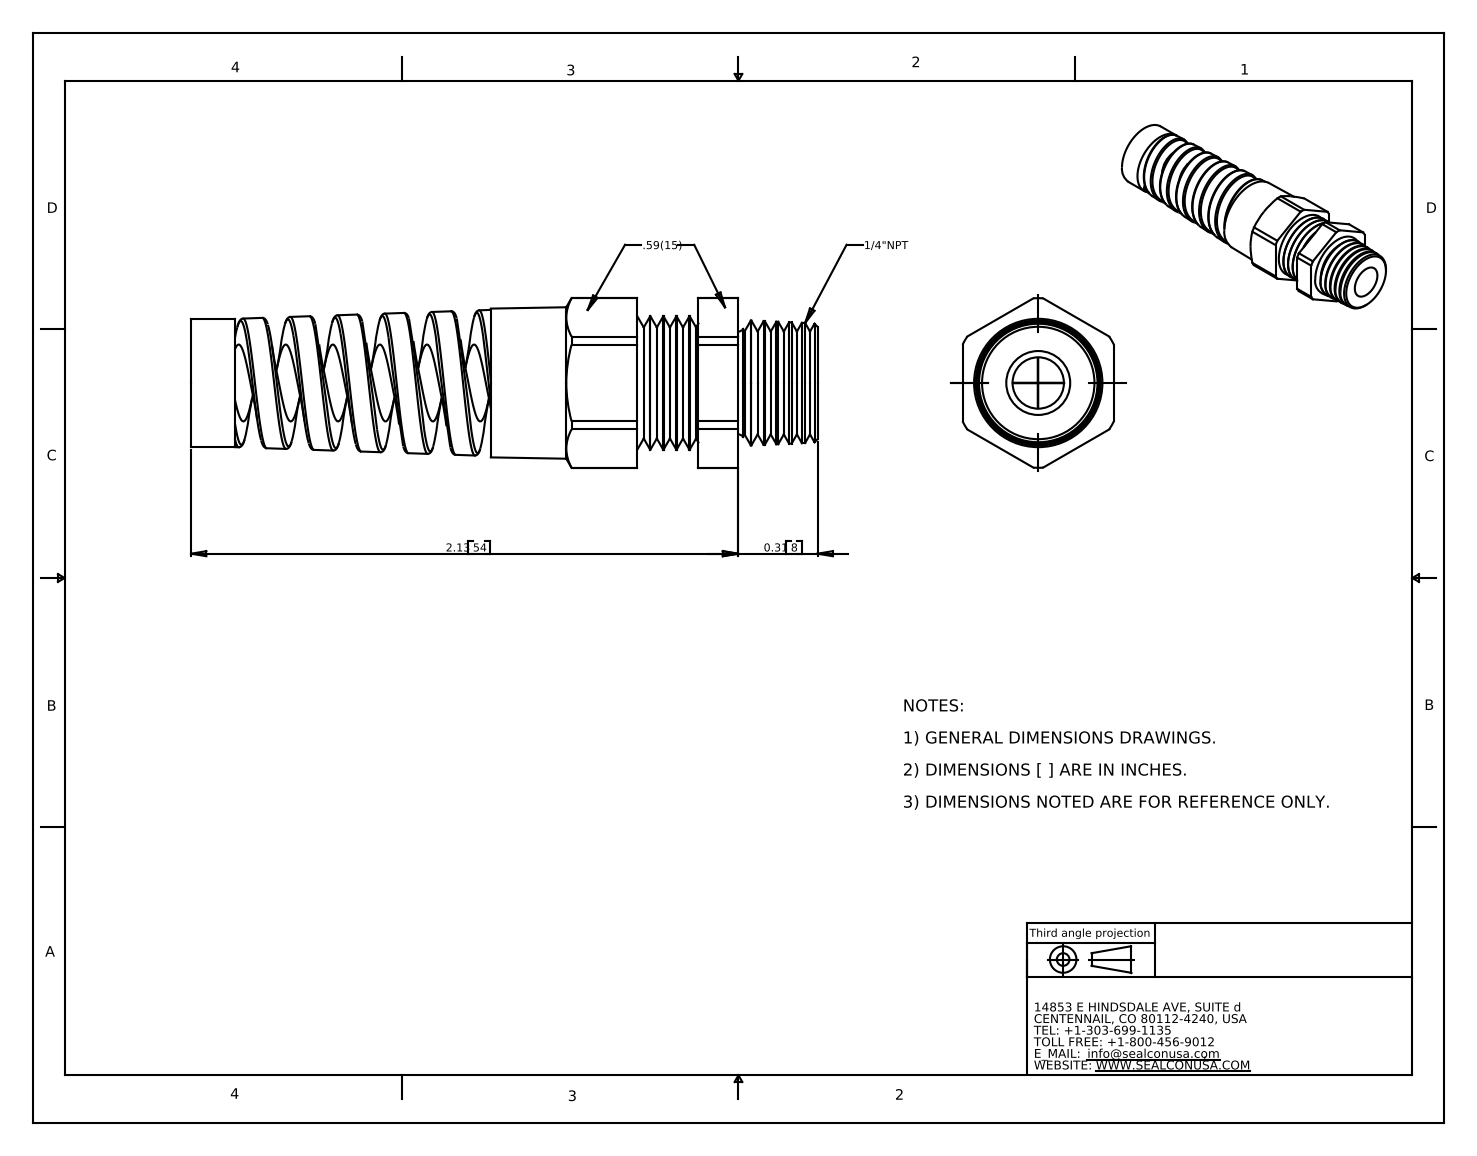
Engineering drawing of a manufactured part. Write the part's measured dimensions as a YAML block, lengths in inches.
part_name: "CF07AR-BK"
step_written_by: "SolidWorks 2007 (CONFIG_CONTROL_DESIGN)"
units: inches
bodies: {solids: 1, faces: 146, planar: 19, cylindrical: 39, other: 88}
overall_size: [2.44, 0.661, 0.59]
volume: 0.356
surface_area: 8.119
round_holes:
  - {diameter: 0.2, count: 1}
  - {diameter: 0.3, count: 1}
round_bosses_or_shafts:
  - {diameter: 0.519, count: 1}
  - {diameter: 0.5, count: 1}
partial_cylinders:
  - {radius: 0.33, count: 1}
face_to_face_distances: [0.59, 1.167, 2.13, 0.963, 2.44, 1.272, 0.31, 1.738, 0.57, 0.392]
